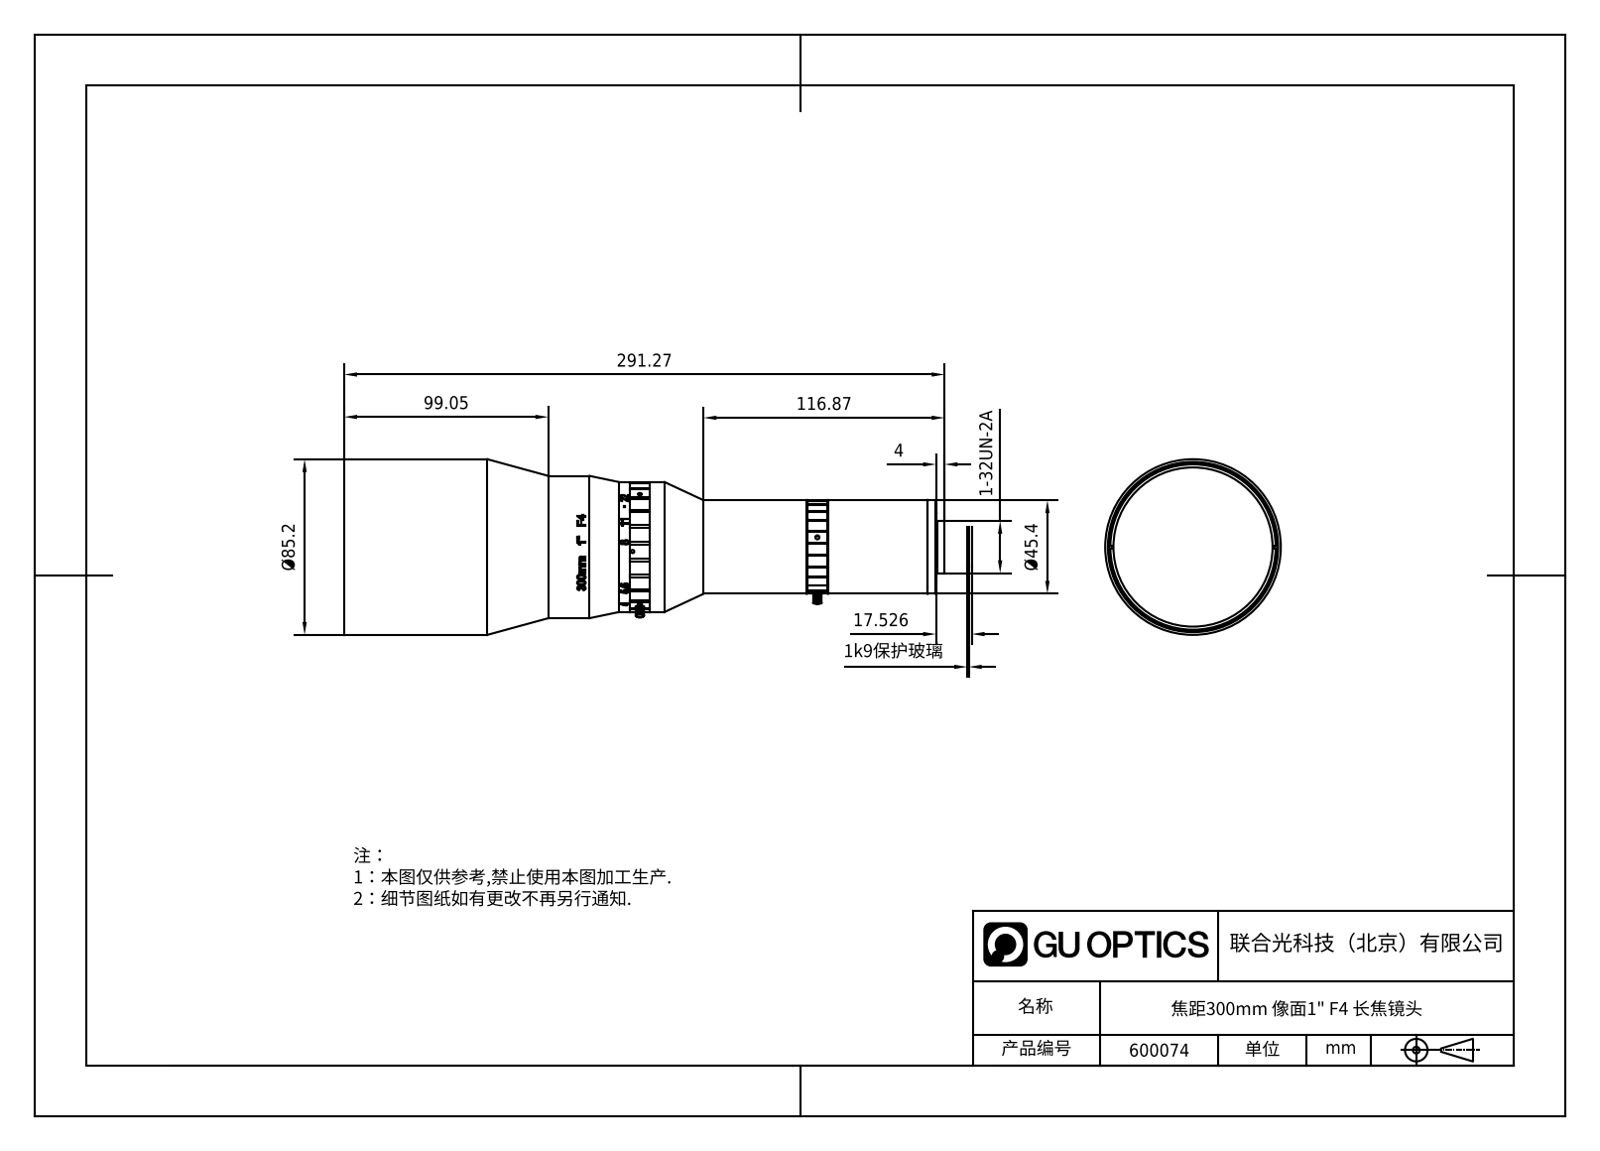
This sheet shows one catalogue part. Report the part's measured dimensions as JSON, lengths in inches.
{"part_name": "600074", "step_written_by": "SolidWorks 2020 (AUTOMOTIVE_DESIGN)", "units": "inches", "bodies": {"solids": 19, "faces": 921, "planar": 346, "cylindrical": 251, "other": 324}, "overall_size": [11.467, 3.354, 3.354], "volume_in3": 58.98, "surface_area_in2": 205.4, "round_holes": [[0.079, 10], [0.081, 4], [0.112, 4], [0.039, 2], [0.764, 1], [0.843, 1], [1.173, 1], [1.528, 1], [1.591, 1], [1.685, 1], [1.728, 1], [1.748, 1]], "round_bosses_or_shafts": [[0.11, 4], [0.079, 4], [3.354, 1], [3.236, 1], [3.016, 1], [2.717, 1], [2.48, 1], [2.268, 1]], "partial_cylinders_radius": [[0.394, 24], [0.591, 24], [0.079, 2], [0.594, 1], [1.236, 1], [1.354, 1]], "face_to_face_distances": [4.975, 0.315, 3.706, 8.681, 10.366, 5.391, 1.685, 4.66, 4.021, 5.706], "hole_center_spacings": [0.705, 0.996, 0.624, 1.032, 1.22, 0.376, 0.48, 1.146]}
